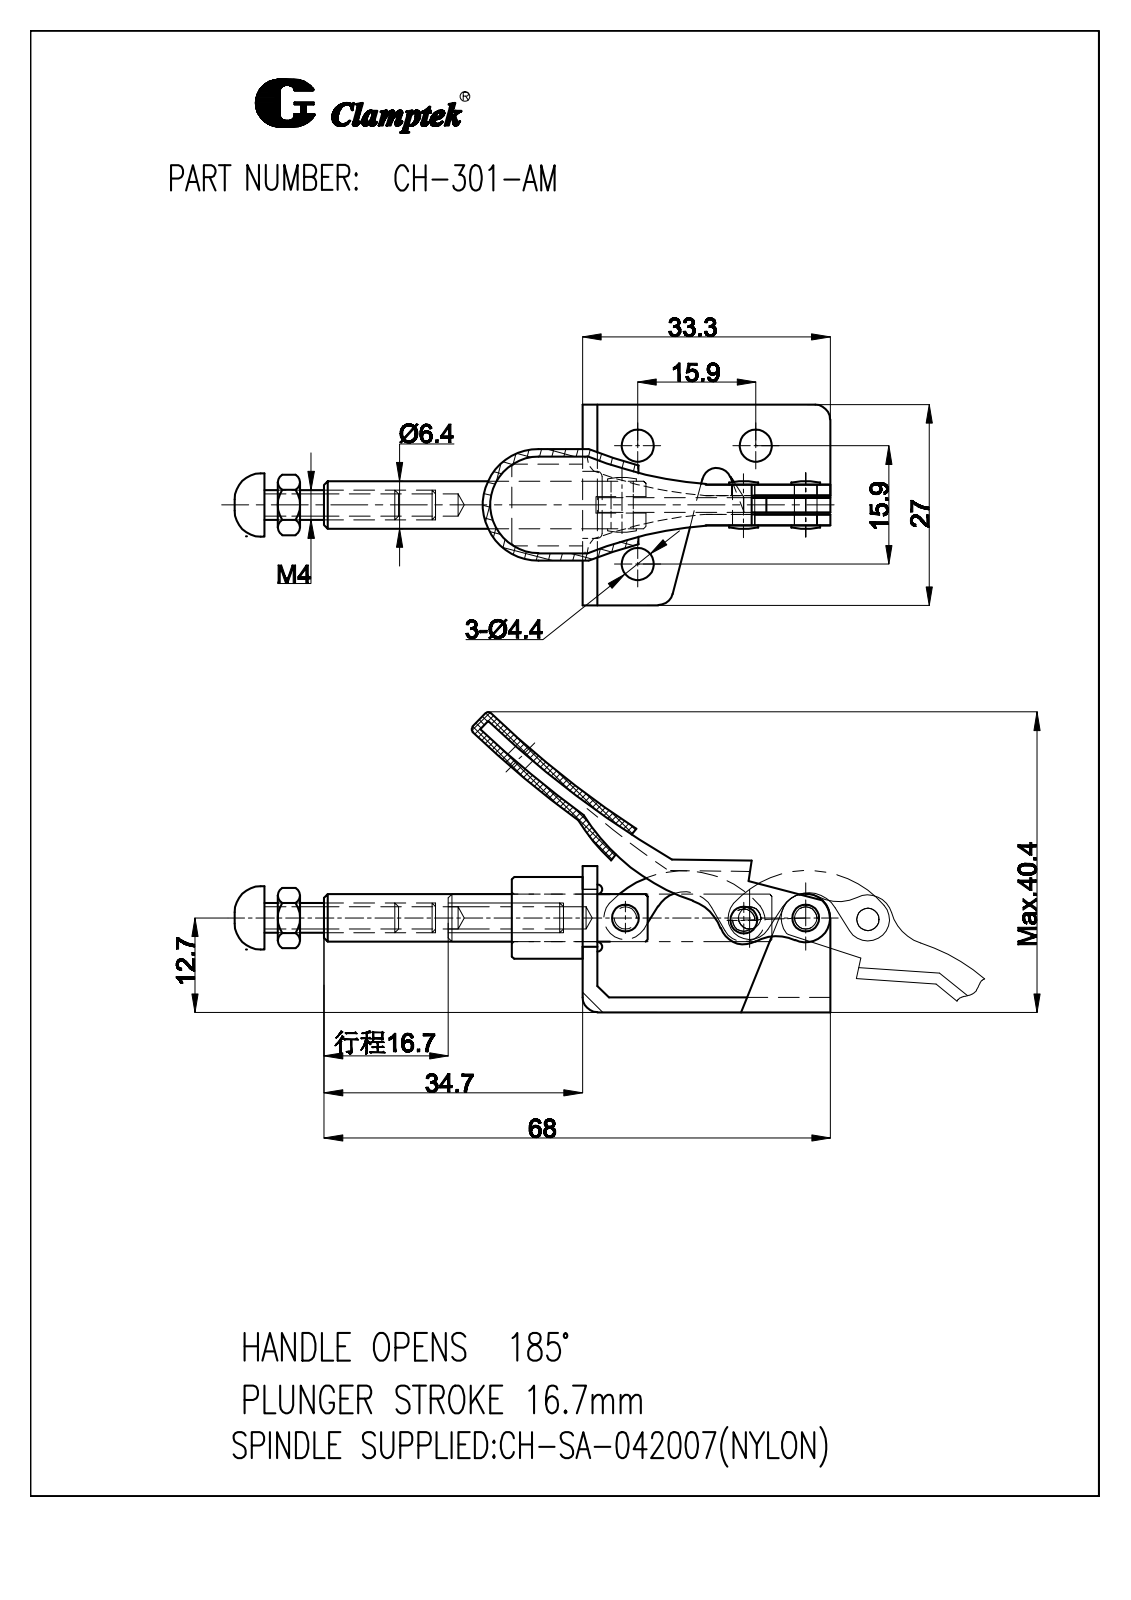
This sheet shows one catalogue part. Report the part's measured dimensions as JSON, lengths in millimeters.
{"part_name": "CH-301-AM-02 CREST STALK; CH-301-AM-05 LEAD SET; CH-301-07; M4 Nut (+8 more)", "step_written_by": "SolidWorks 2010 (CONFIG_CONTROL_DESIGN)", "units": "millimeters", "bodies": {"solids": 11, "faces": 766, "planar": 260, "cylindrical": 234, "other": 272}, "overall_size": [79.02, 38.41, 27], "volume_mm3": 5662, "surface_area_mm2": 9074, "round_holes": [[3, 3], [4.4, 3], [1.17, 1], [2.4, 1], [3.2, 1], [6.4, 1], [7.7, 1]], "round_bosses_or_shafts": [[11, 1], [4, 1], [1.03, 1]], "partial_cylinders_radius": [[0.3, 14], [1, 5], [2, 5], [1.5, 4], [1.4, 3], [2.9, 2], [3, 2], [3.3, 2]], "face_to_face_distances": [2, 0.4, 2.1, 2.5, 1.5, 0.38, 4, 2.12, 1.7, 1.72], "hole_center_spacings": [15.9, 8.19, 8.35, 22.49, 24.22]}
